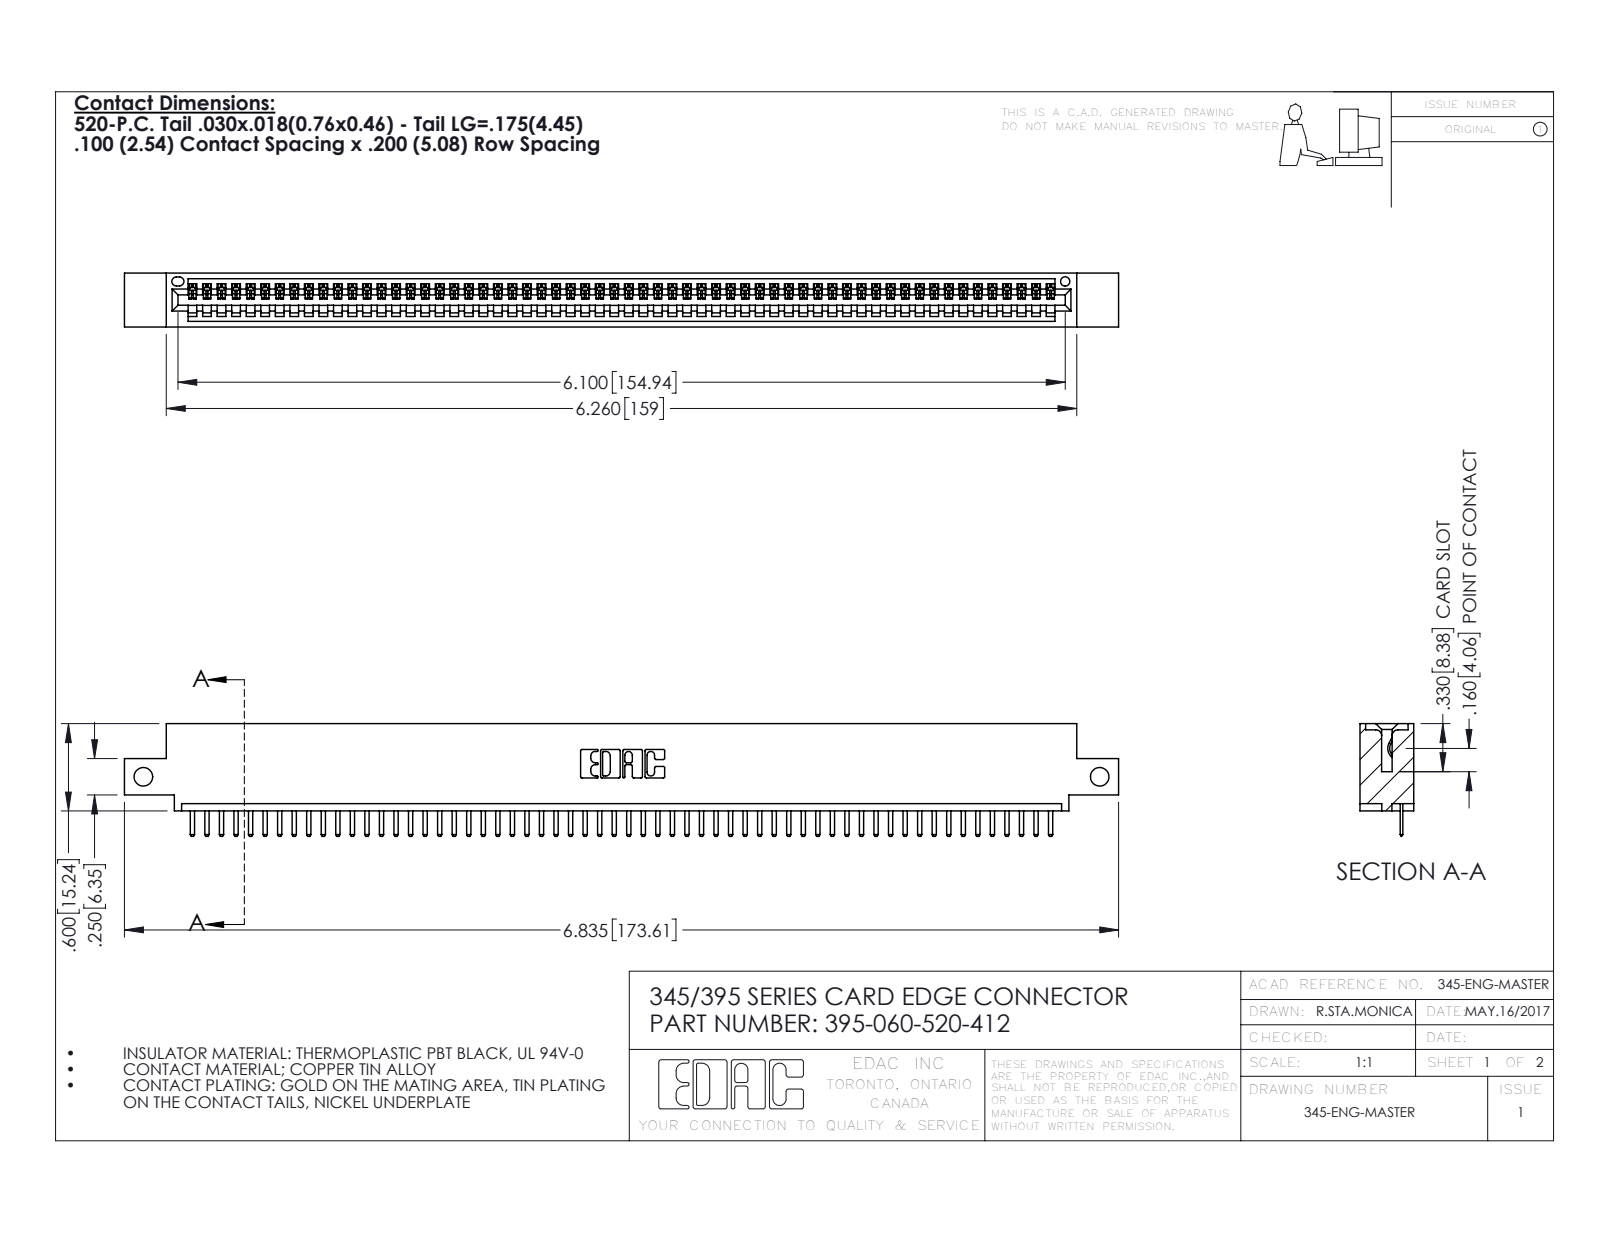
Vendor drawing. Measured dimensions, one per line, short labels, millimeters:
name: 345-292-001_345-293-120; 345 Part_0.110 Offset - Side Mount; 395-060-520-412
written by: SolidWorks 2016 (CONFIG_CONTROL_DESIGN)
unit: mm
bodies: 61 solids, 3850 faces (2604 planar, 1246 cylindrical, 0 other)
size: 173.6 × 19.7 × 9.4
volume: 16 300 mm³; area: 21 280 mm²
holes: 2× ⌀3.3, 1× ⌀1.6
rounds: 122× R0.3, 120× R0.2, 22× R0.3, 6× R0.2, 6× R0.8, 3× R0.7, 2× R0.8, 2× R1
face distances: 7.6, 1.8, 9.4, 5.1, 2.5, 6.9, 0.6, 5.7, 1.8, 3.8
hole spacings: 167
